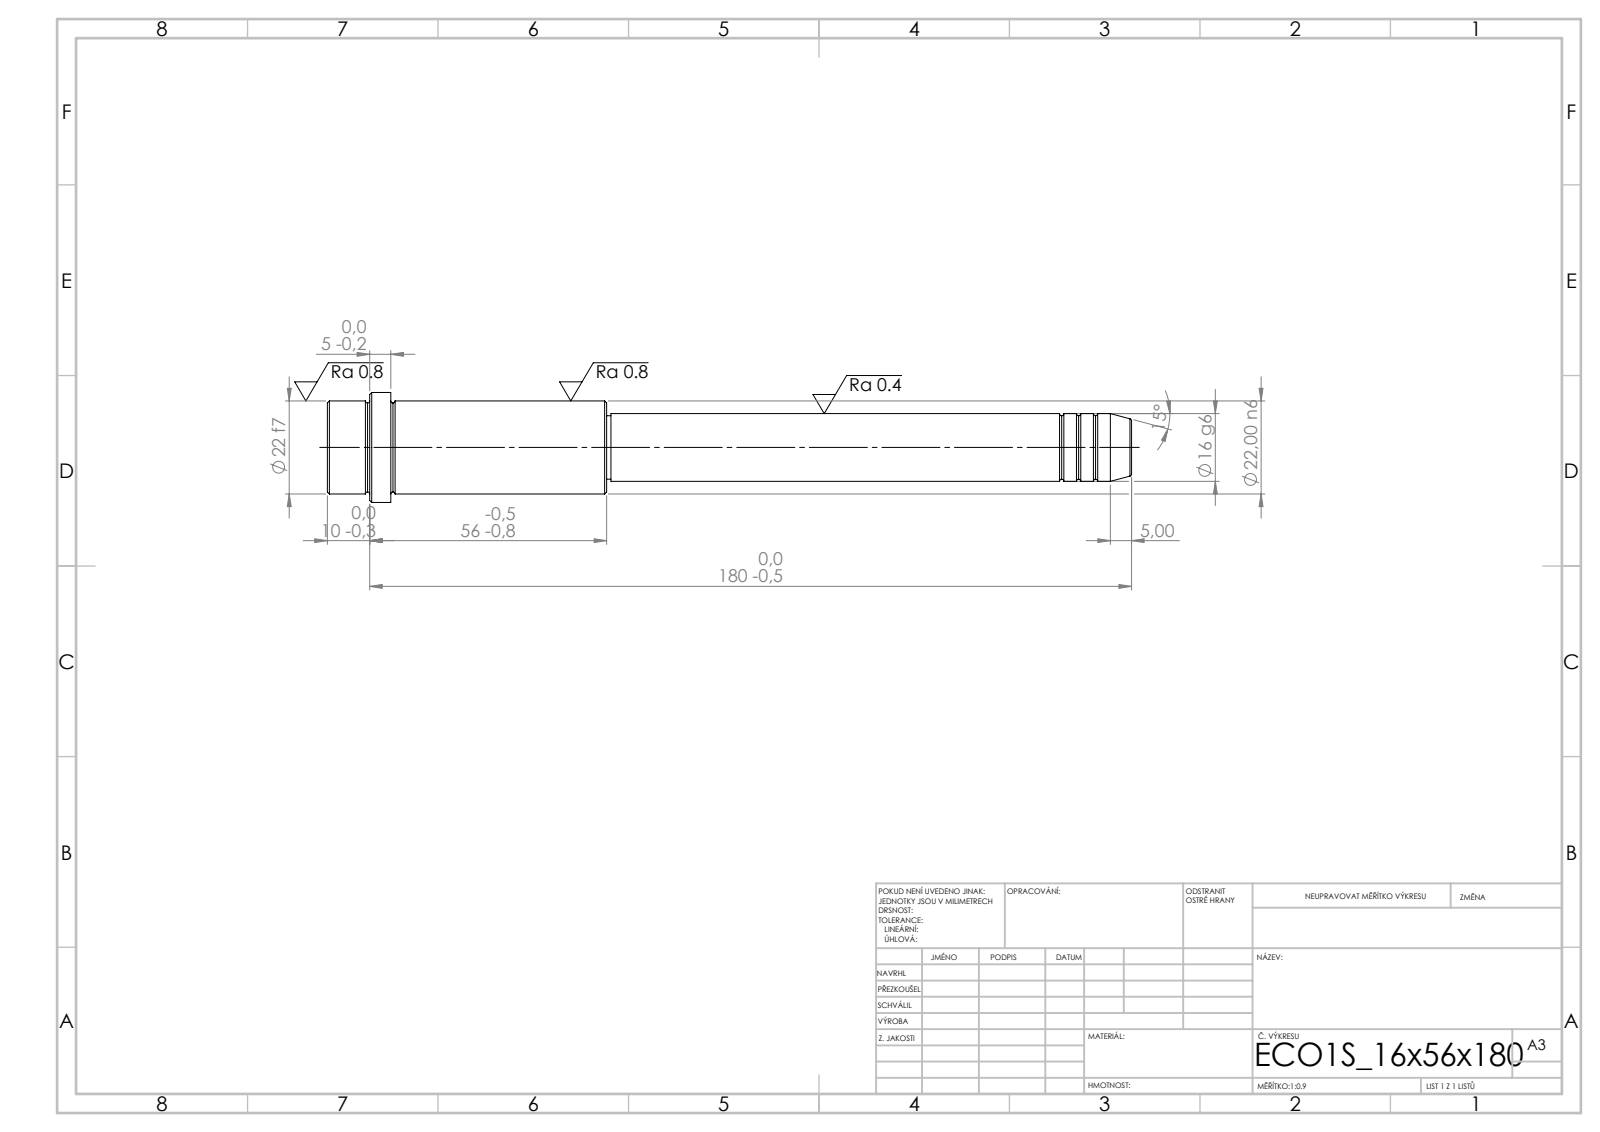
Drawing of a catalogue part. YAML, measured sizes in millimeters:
step_written_by: "SolidWorks 2019 (CONFIG_CONTROL_DESIGN)"
units: millimeters
bodies: {solids: 1, faces: 52, planar: 6, cylindrical: 16, other: 30}
overall_size: [190, 26, 26]
volume: 50452
surface_area: 11969
round_bosses_or_shafts:
  - {diameter: 26, count: 1}
  - {diameter: 22, count: 1}
  - {diameter: 16, count: 1}
  - {diameter: 15, count: 1}
face_to_face_distances: [66, 51, 15, 124, 175, 190, 180, 56, 5, 10]
